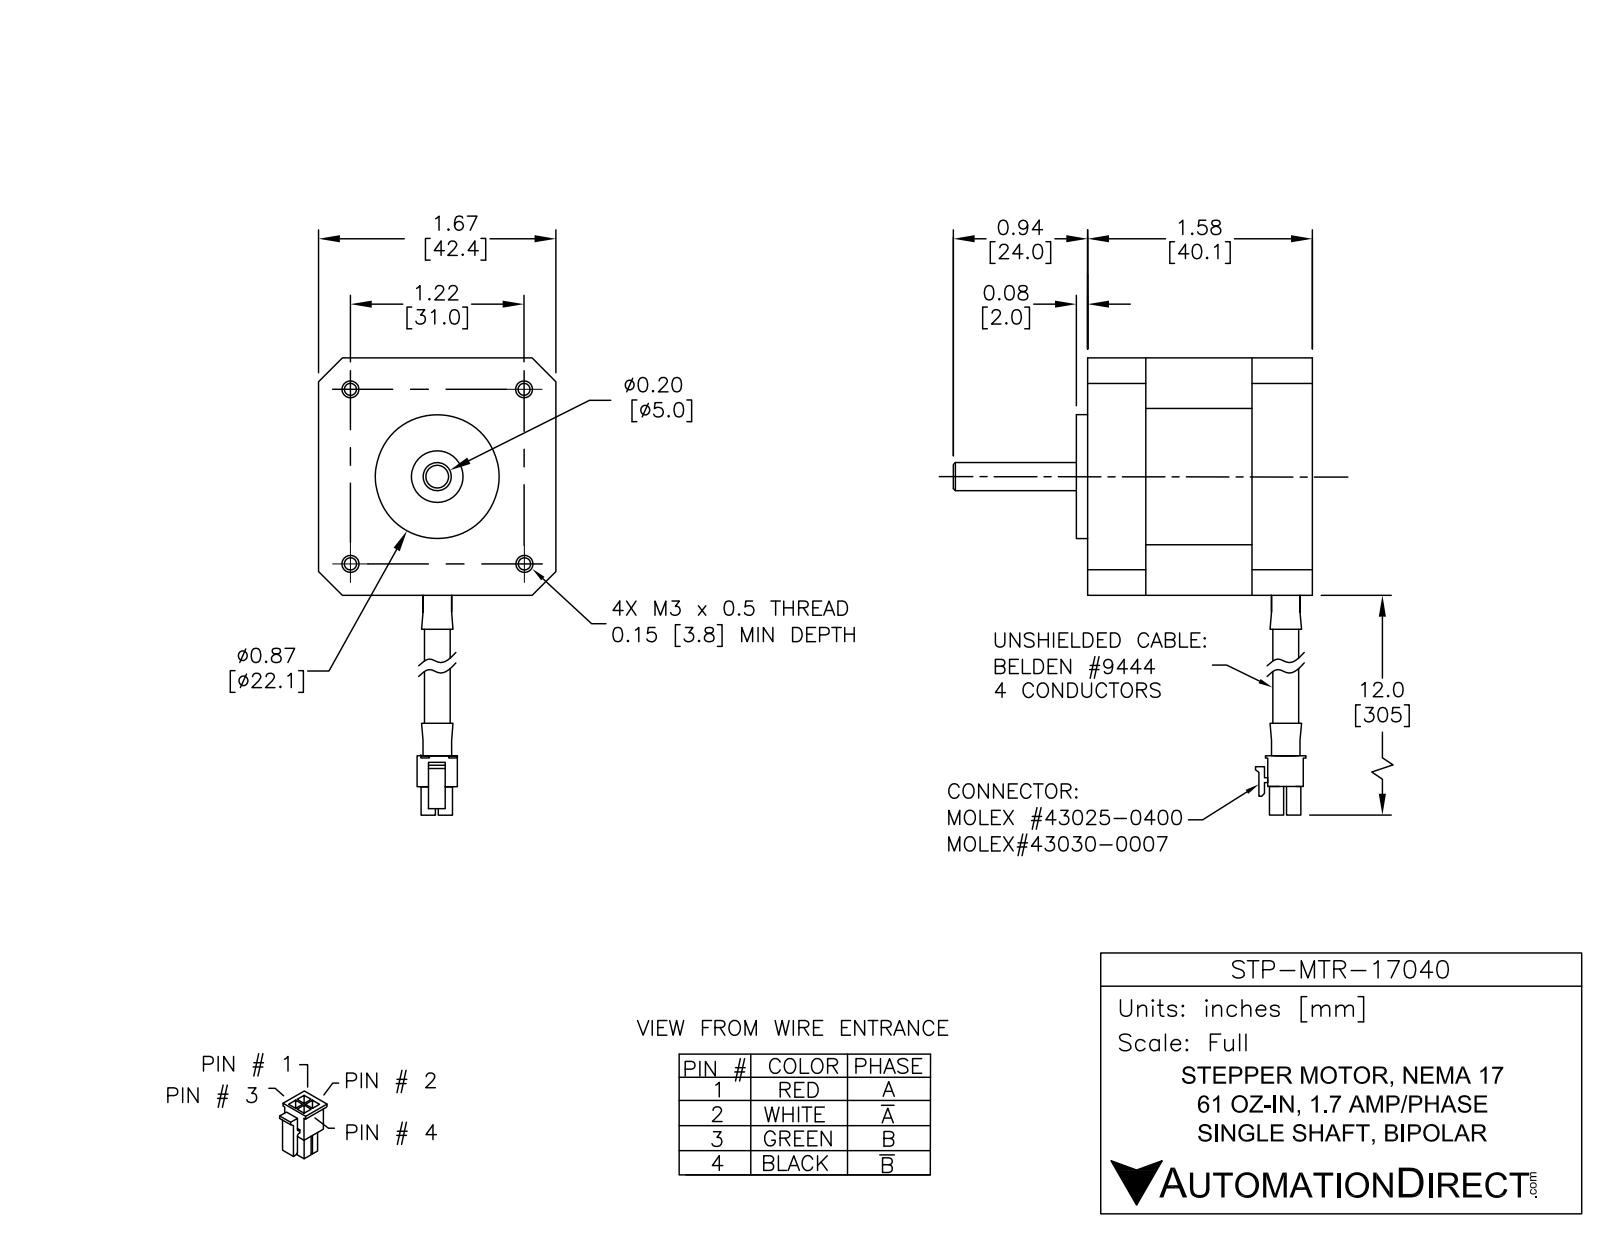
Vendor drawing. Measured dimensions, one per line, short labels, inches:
name: STP-MTR-17040
written by: SolidWorks 2014 (AUTOMOTIVE_DESIGN)
unit: in
bodies: 1 solid, 40 faces (16 planar, 24 cylindrical, 0 other)
size: 5.266 × 2.51 × 1.66
volume: 4.295 in³; area: 19.34 in²
holes: 4× ⌀0.086
bosses: 4× ⌀0.038, 1× ⌀0.866, 1× ⌀0.197
rounds: 1× R1.06
face distances: 1.66, 1.57, 1.649, 0.079, 2.51, 0.94, 0.861, 0.03, 1.54, 1.619
hole spacings: 1.22, 1.725
